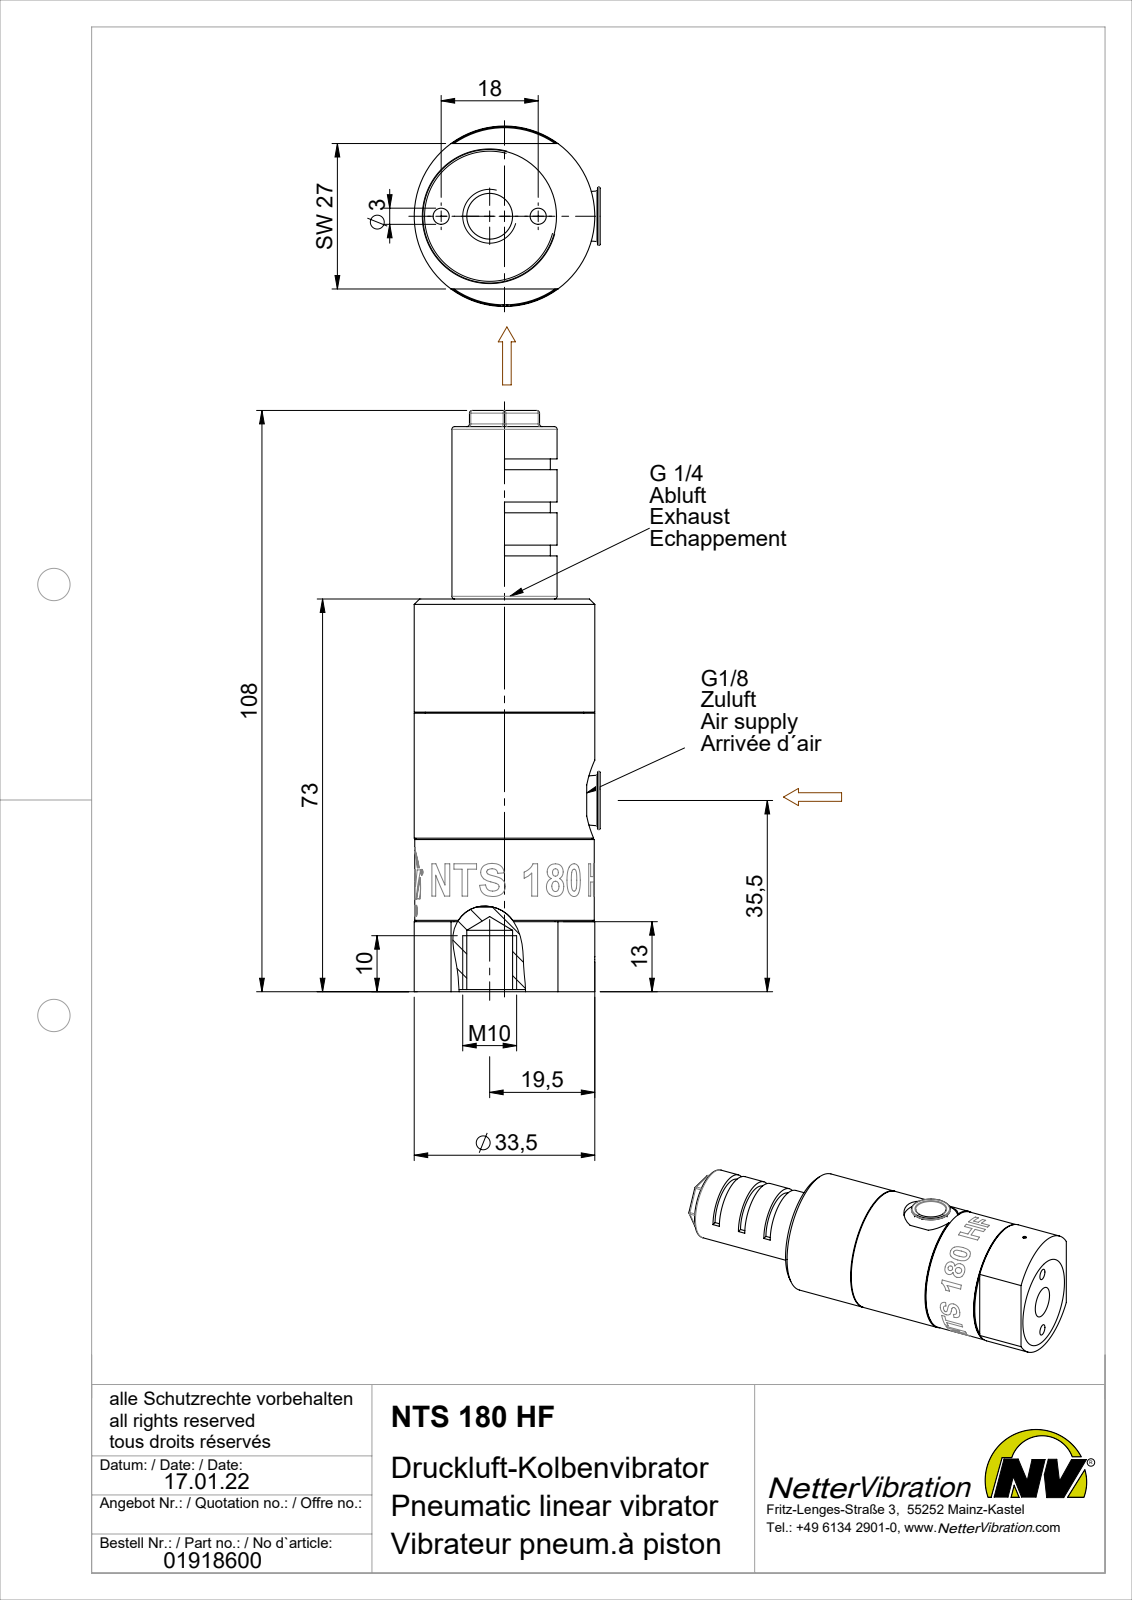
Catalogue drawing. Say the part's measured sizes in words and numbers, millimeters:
The part is named "NTS 180 HF Kolbenvibrator #01918600". Its 3-D file was written by "SolidWorks 2015 (AUTOMOTIVE_DESIGN)". It is 6 solids with 250 faces: 48 planar, 155 cylindrical and 47 other. Overall it measures 107.9 by 33.5 by 33.5 millimeters. Its volume is 68 898 cubic millimeters and its surface area 24 961 square millimeters. Round holes: 4 of diameter 3, 1 of diameter 1, 1 of diameter 8.5, 1 of diameter 8.57, 1 of diameter 11.8, 1 of diameter 11.9, 1 of diameter 24.8, 1 of diameter 25.2, 1 of diameter 28, 1 of diameter 32.9. Round bosses or shafts: 1 of diameter 33.5, 1 of diameter 33.3, 1 of diameter 29.4, 1 of diameter 29, 1 of diameter 27.5, 1 of diameter 25, 1 of diameter 19.5, 1 of diameter 18.5. Partial cylindrical surfaces (rounded edges, fillets, slot ends): 22 of radius 0.5, 1 of radius 7.5, 1 of radius 8.5. The main face-to-face distances are 11.9, 56.2, 55.9, 44, 44.3, 72.5, 60.6, 16.6, 16.3, 9.3. The hole center spacings are 9, 13, 1.25, 2.75, 6.25, 6.75, 10.25, 11.75.
